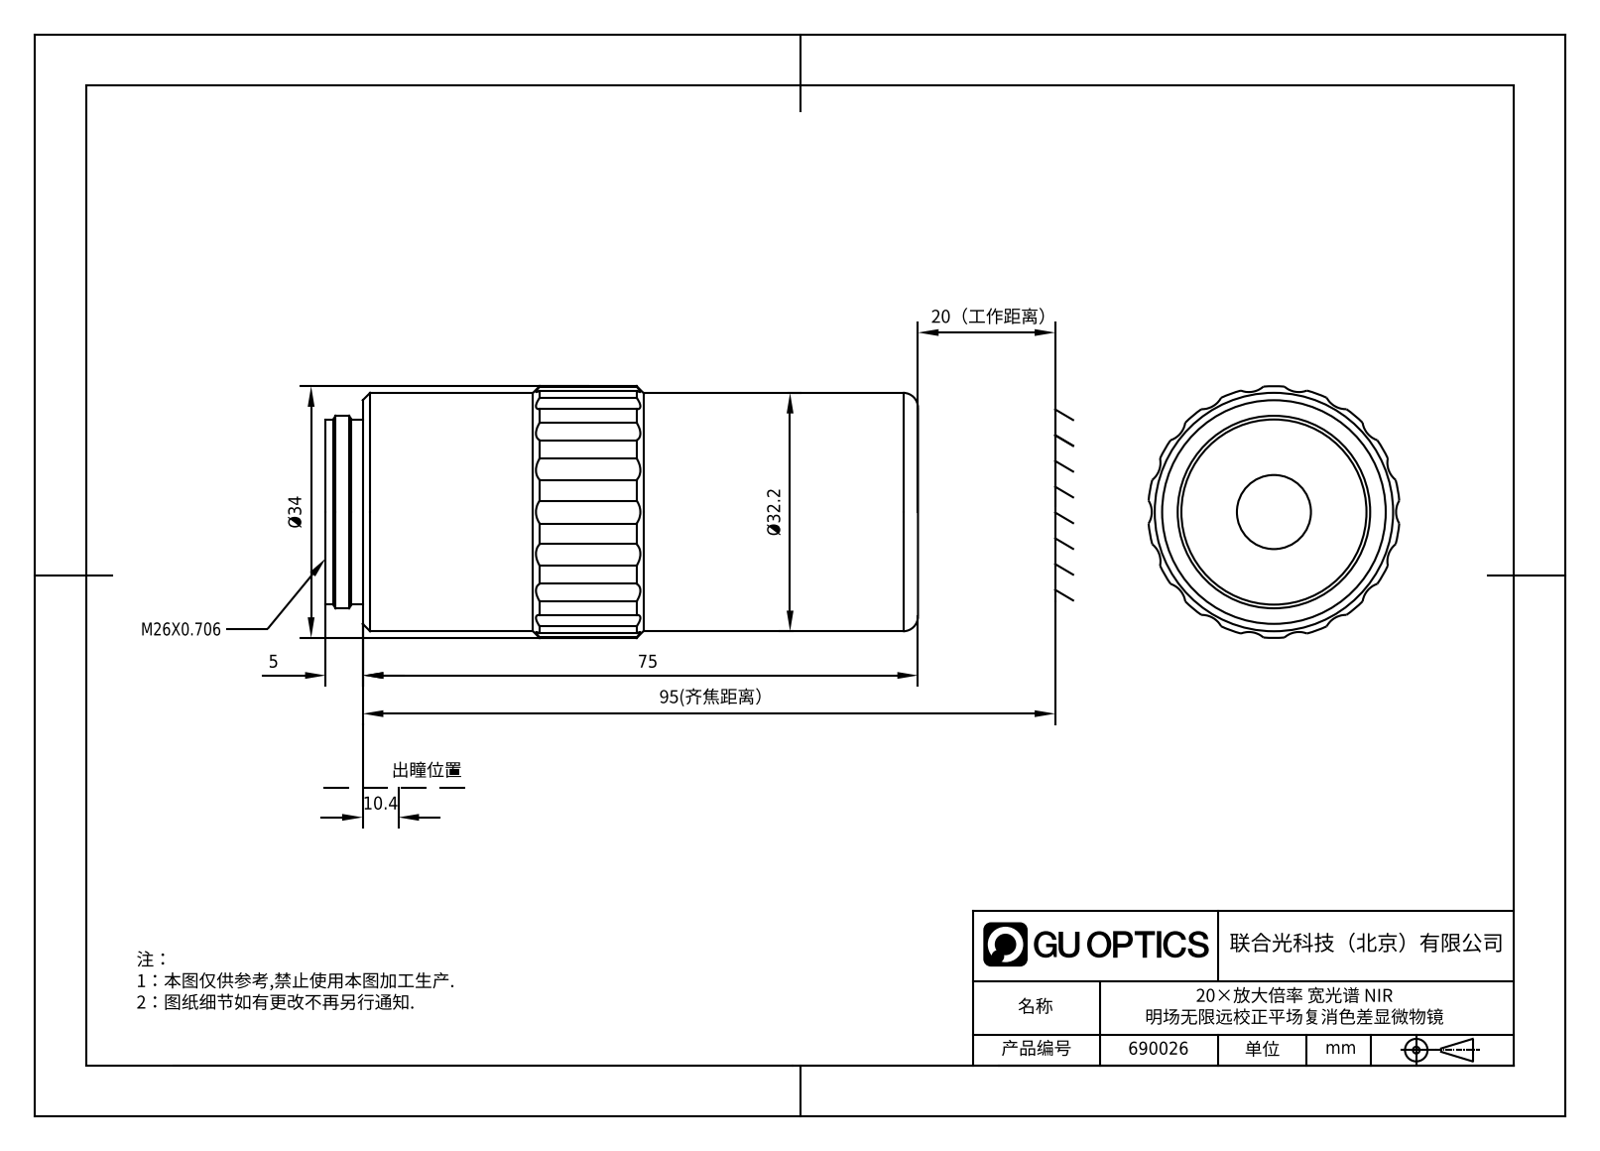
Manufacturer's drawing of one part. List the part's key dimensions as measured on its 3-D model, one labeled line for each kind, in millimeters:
Part name (STEP PRODUCT): 690026
STEP written by: SolidWorks 2020 (CONFIG_CONTROL_DESIGN)
Units: millimetres
Bodies: 1 solid, 55 faces (6 planar, 43 cylindrical, 6 other)
Overall size (bounding box): 80 × 34 × 33.86
Volume: 64 111 mm³ · Surface area: 9 797 mm²
Round holes (diameter × count): ⌀10 ×1, ⌀21 ×1
Round bosses / shafts (diameter × count): ⌀32.2 ×1, ⌀26 ×1, ⌀25 ×1
Partial cylindrical surfaces — rounded edges, fillets, slot ends (radius × count): R3 ×18, R17 ×1
Main face-to-face distances: 79, 1, 80, 5, 74, 75, 4, 78, 43, 42
